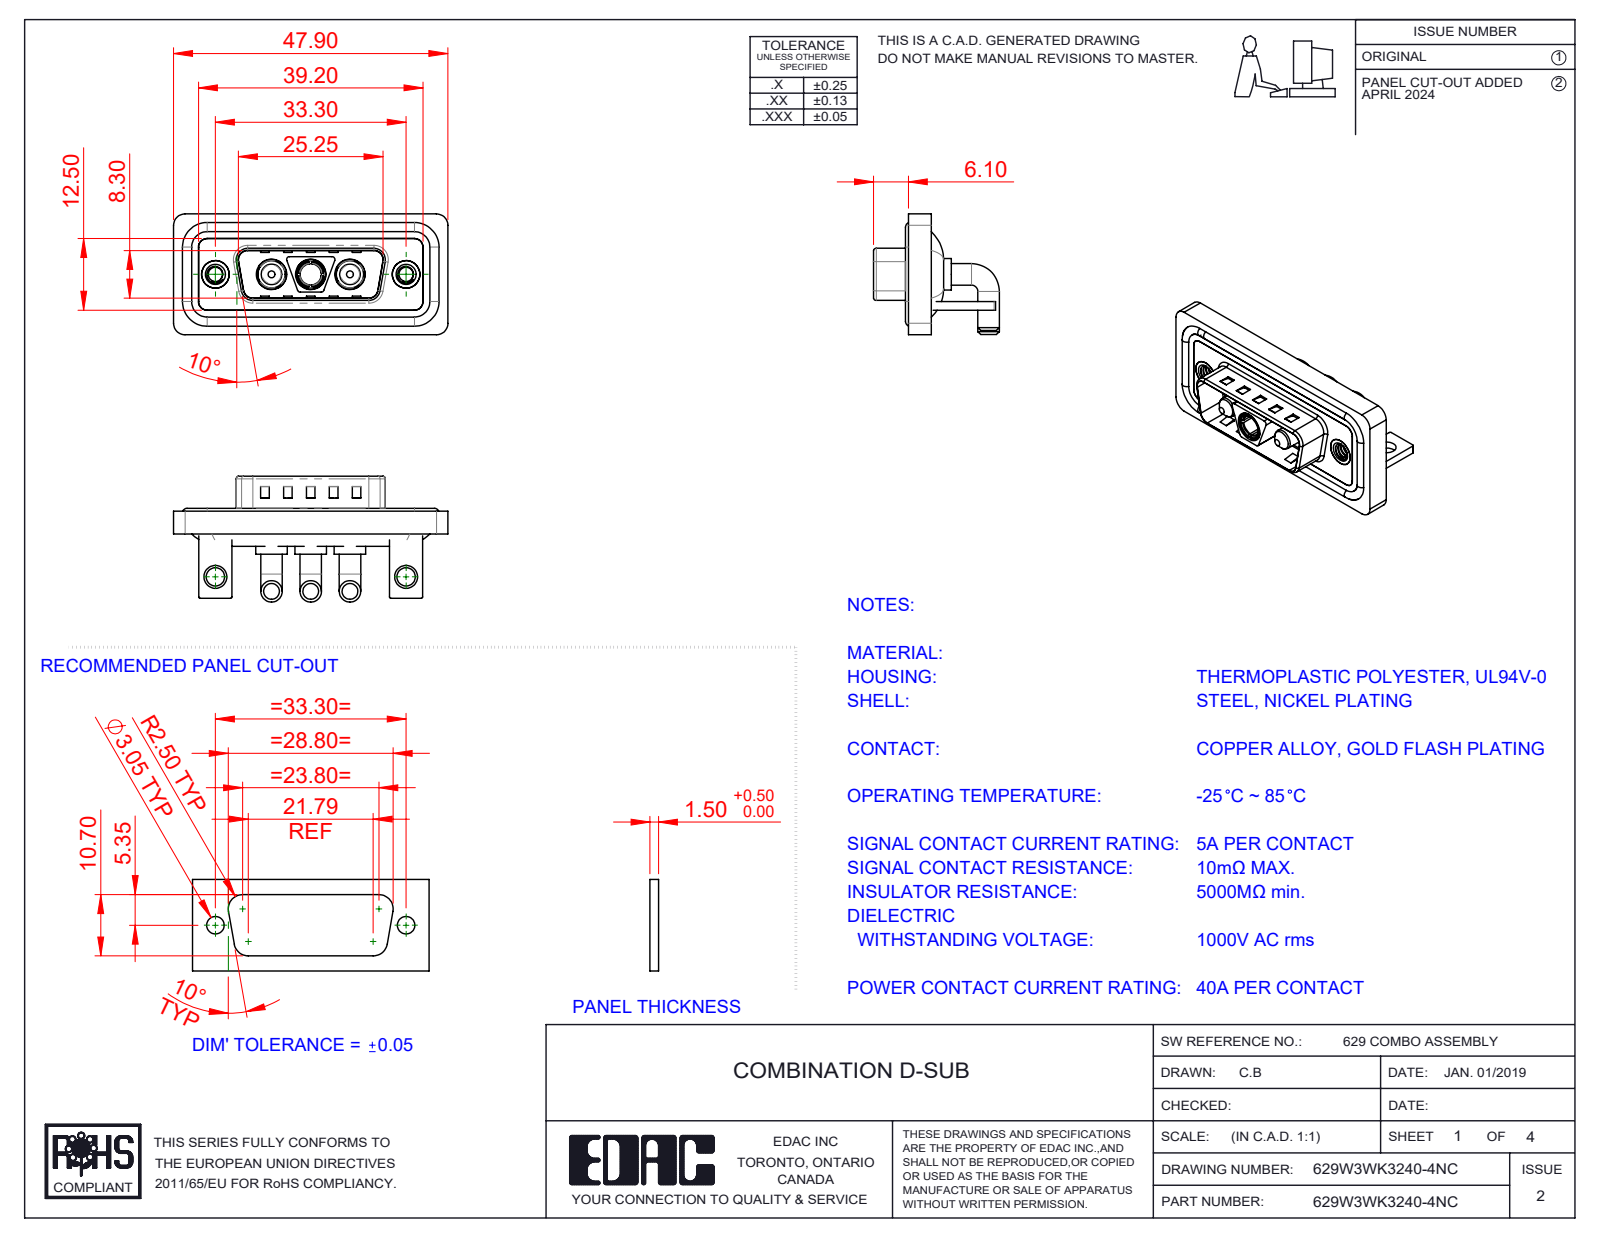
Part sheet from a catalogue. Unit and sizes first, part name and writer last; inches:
Units: inches
Overall size (bounding box): 1.886 × 0.865 × 0.831
Round holes (diameter × count): ⌀0.191 ×3, ⌀0.209 ×3, ⌀0.098 ×2, ⌀0.126 ×2, ⌀0.157 ×2, ⌀0.189 ×2, ⌀0.197 ×2, ⌀0.146 ×1
Round bosses / shafts (diameter × count): ⌀0.148 ×6, ⌀0.063 ×4, ⌀0.217 ×3, ⌀0.205 ×3, ⌀0.187 ×3, ⌀0.193 ×2, ⌀0.142 ×2, ⌀0.195 ×1
Partial cylindrical surfaces — rounded edges, fillets, slot ends (radius × count): R0.079 ×21, R0.059 ×18, R0.01 ×16, R0.02 ×13, R0.063 ×8, R0.024 ×4, R0.026 ×4, R0.035 ×4
Main face-to-face distances: 0.016, 0.059, 0.031, 0.114, 0.043, 0.083, 0.146, 0.063, 0.047, 0.177
Hole centre spacings: 0.27, 0.386, 0.656, 0.925, 1.311, 0.539
Volume: 0.389 in³ · Surface area: 15.71 in²
Bodies: 15 solids, 659 faces (251 planar, 274 cylindrical, 134 other)
Part name (STEP PRODUCT): Power Pin_40A RA; 629Combo Threaded Rivet_B; 629Combo Shell Front_15 Contacts; 629Combo Stabilizer Bracket (+5 more)
STEP written by: SolidWorks 2023 (CONFIG_CONTROL_DESIGN)
